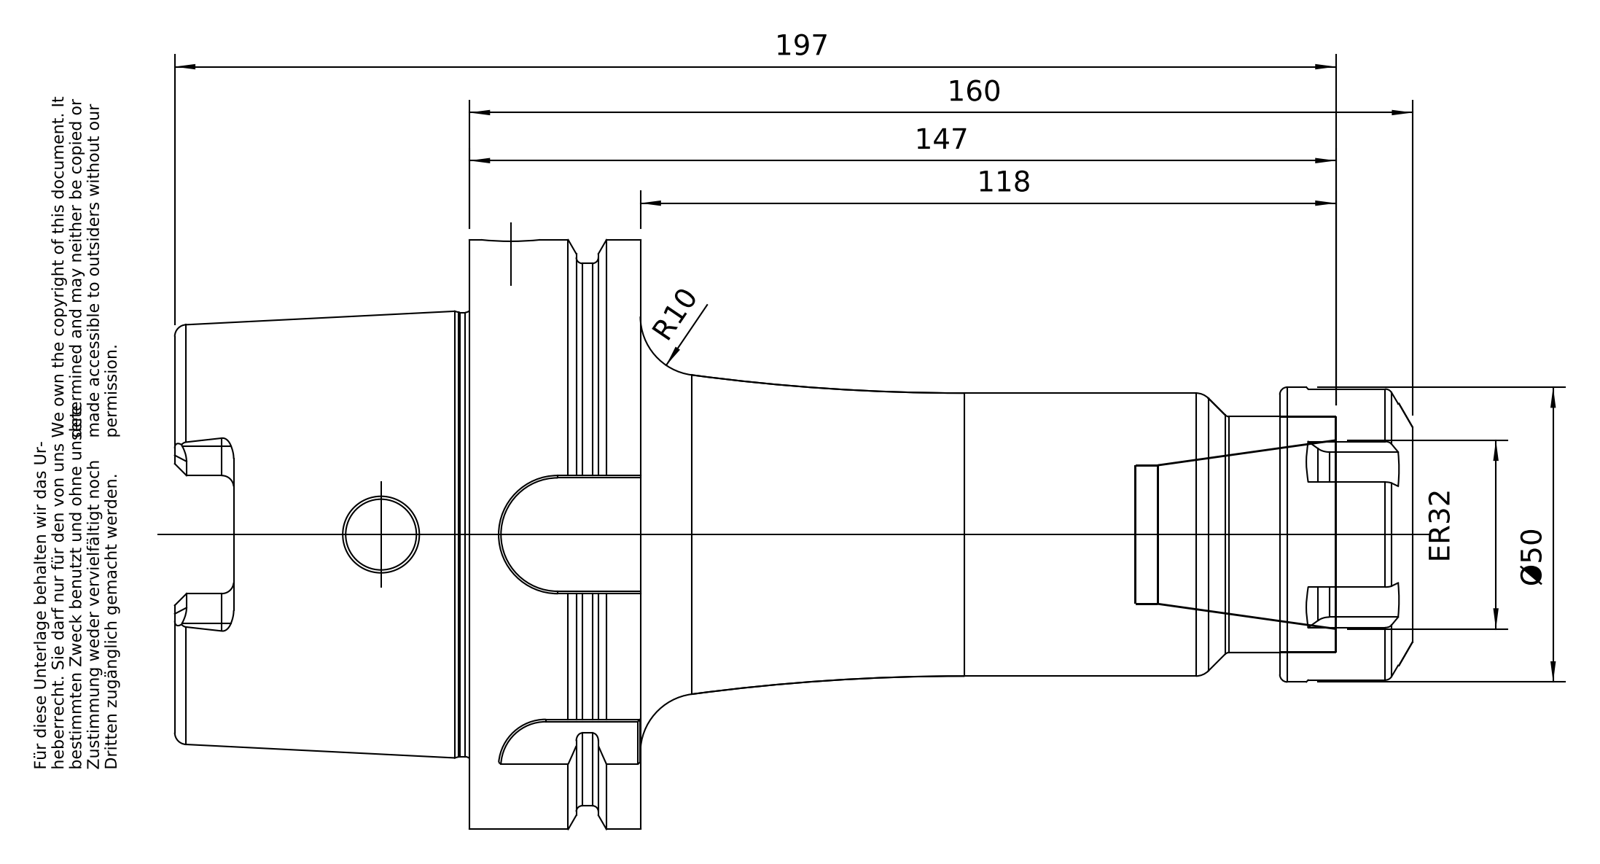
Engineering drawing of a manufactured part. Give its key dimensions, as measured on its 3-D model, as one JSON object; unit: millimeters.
{"part_name": "A100-022-32; 83-912-32; A100-022-32_ASM", "step_written_by": "PRO/ENGINEER BY PARAMETRIC TECHNOLOGY CORPORATION, 2010430 (CONFIG_CONTROL_DESIGN)", "units": "millimeters", "bodies": {"solids": 2, "faces": 227, "planar": 78, "cylindrical": 60, "other": 89}, "overall_size": [210, 100, 100], "volume_mm3": 492292, "surface_area_mm2": 76294, "round_holes": [[10, 1], [12, 1], [22.5, 1], [23.5, 1], [24, 1], [24.32, 1], [24.5, 1], [53, 1], [63, 1]], "round_bosses_or_shafts": [[100, 1], [92, 1], [75.36, 1], [50, 1], [48, 1], [40, 1]], "partial_cylinders_radius": [[2, 6], [2.7, 6], [5, 4], [8, 1], [10.02, 1], [11.02, 1]], "face_to_face_distances": [29, 137.5, 108.5, 12.5, 16.5, 125, 160, 147.5, 131, 22.5]}
